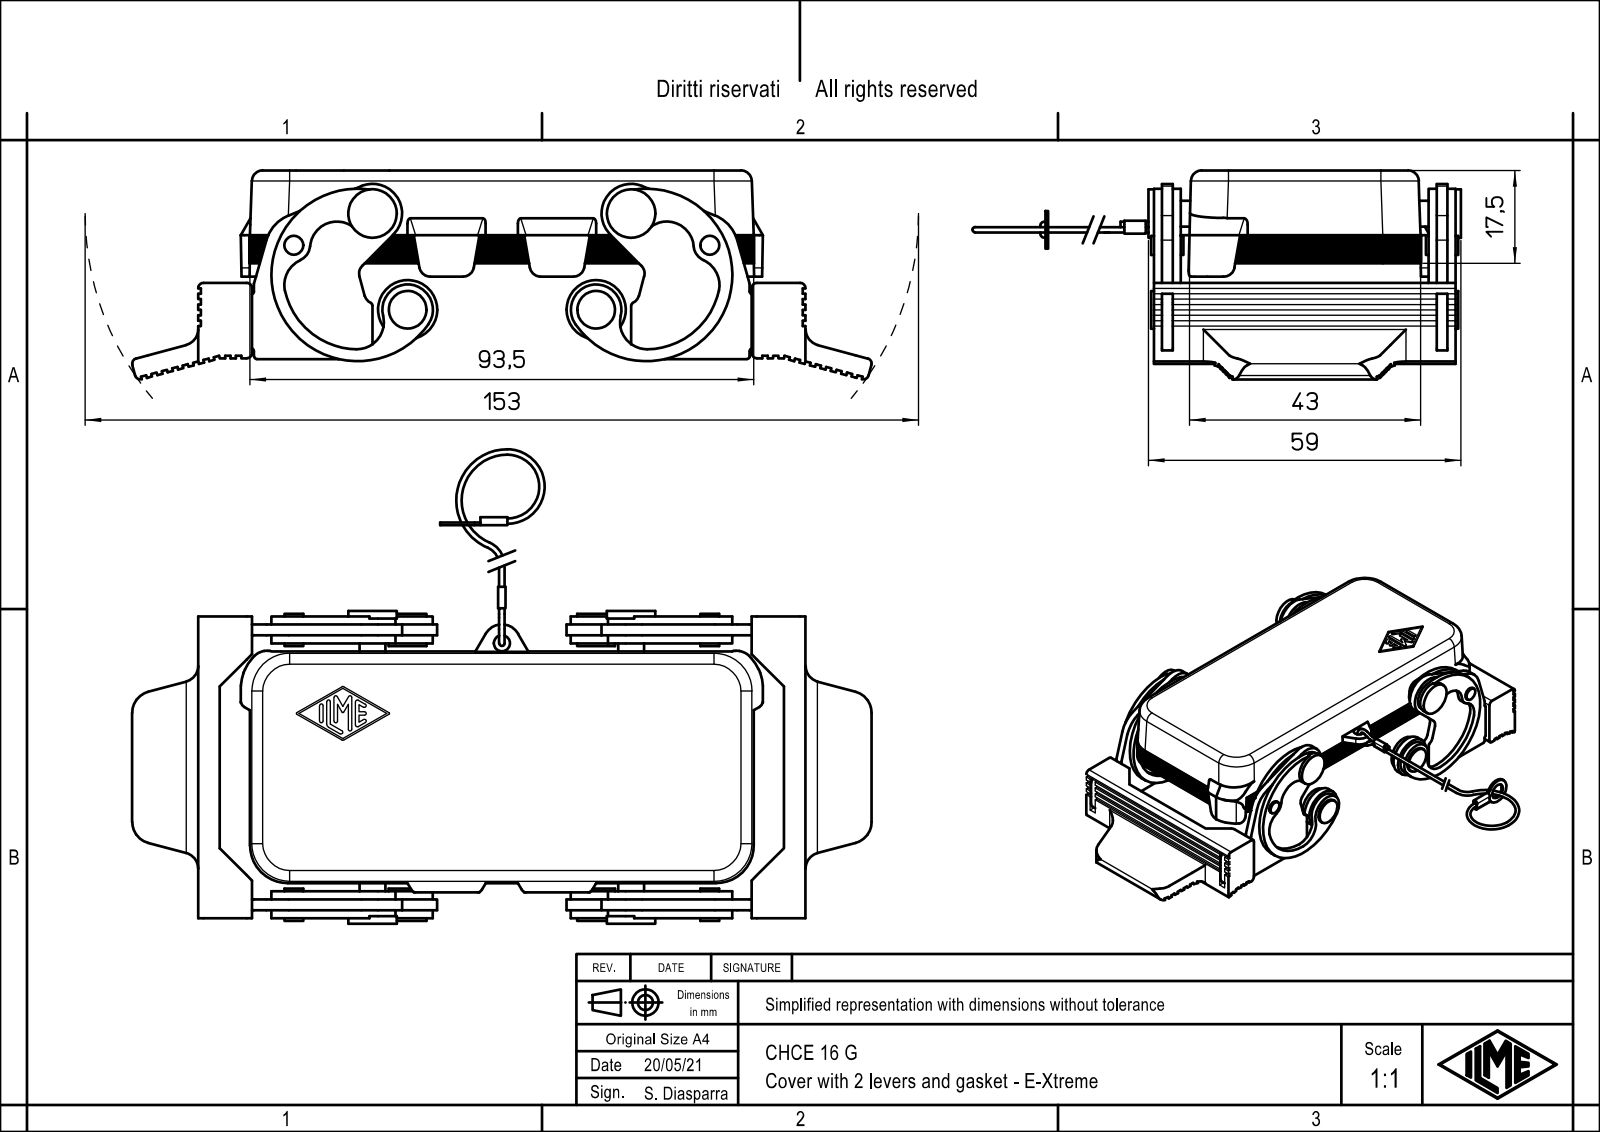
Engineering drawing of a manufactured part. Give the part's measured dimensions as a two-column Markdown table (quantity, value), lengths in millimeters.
| quantity | value |
| --- | --- |
| part name | CHCE_16_G |
| STEP written by | Creo Elements/Direct Modeling 20.1B 02-Apr-2019 (C) Parametric Technology GmbH (AUTOMOTIVE_DESIGN) |
| units | millimeters |
| bodies | 1 solid, 981 faces (604 planar, 331 cylindrical, 46 other) |
| overall size | 225.77 × 137.25 × 39.08 |
| volume | 46 328 mm³ |
| surface area | 36 814 mm² |
| round holes (diameter × count) | 4 × 3, 3.1 × 2, 5 × 2, 3 × 1 |
| round bosses / shafts (diameter × count) | 1 × 5, 7 × 3, 11 × 2, 9 × 2, 4.8 × 2, 3.5 × 2, 3 × 2 |
| partial cylindrical surfaces (radius × count) | 0.33 × 15, 2 × 15, 3 × 14, 1 × 12, 0.5 × 8, 1.5 × 6, 5 × 6, 7 × 6 |
| main face-to-face distances | 3.5, 51, 2, 2.5, 1.5, 7, 42, 9, 44, 45.5 |
| hole center spacings | 19.11, 24.25, 34.07, 57.36, 69.03, 91.2, 35, 77.2 |
